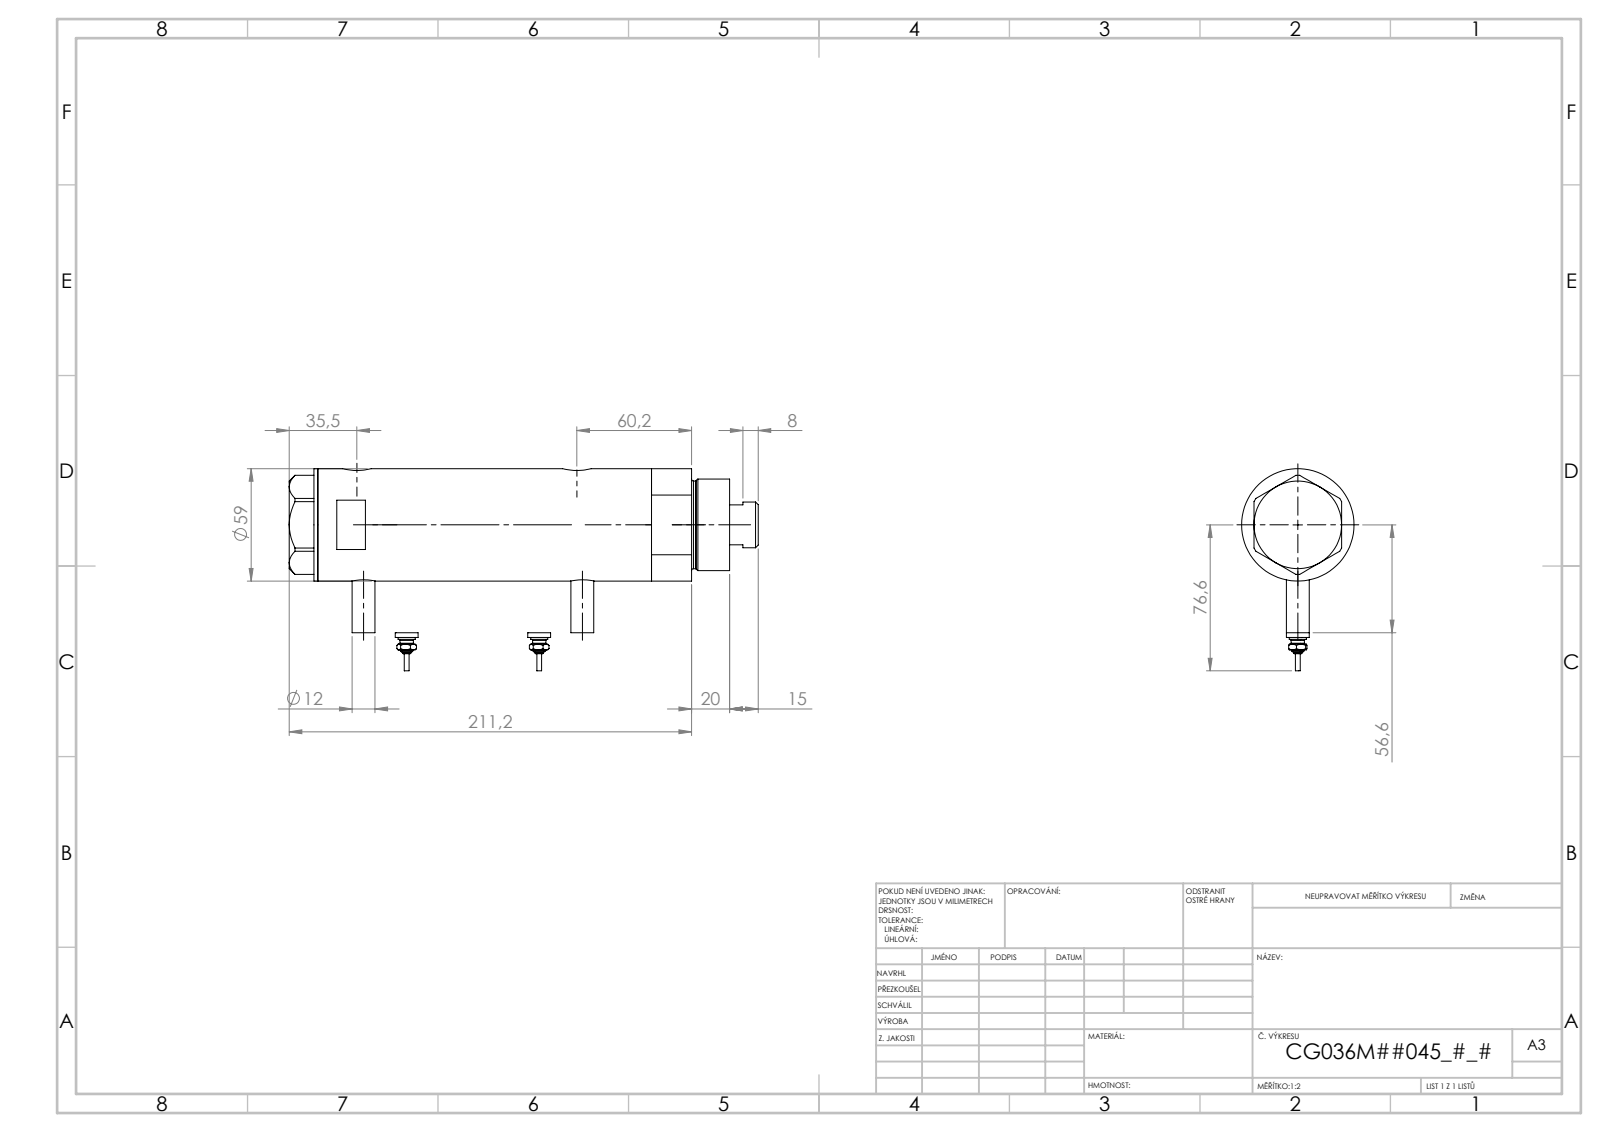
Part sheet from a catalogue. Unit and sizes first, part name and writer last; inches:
Units: inches
Overall size (bounding box): 8.206 × 3.594 × 2.323
Round holes (diameter × count): ⌀0.197 ×2, ⌀0.383 ×2, ⌀0.492 ×2, ⌀0.591 ×2, ⌀0.335 ×1, ⌀0.984 ×1, ⌀1.043 ×1, ⌀1.417 ×1, ⌀1.575 ×1, ⌀2.047 ×1
Round bosses / shafts (diameter × count): ⌀0.472 ×3, ⌀0.354 ×2, ⌀0.276 ×2, ⌀0.171 ×2, ⌀0.094 ×2, ⌀2.323 ×1, ⌀1.89 ×1, ⌀1.811 ×1
Main face-to-face distances: 3.104, 0.591, 4.62, 4.029, 7.615, 1.516, 0.925, 3.104, 1.515, 0.925
Hole centre spacings: 0.114, 0.138, 3.037, 3.152, 3.175, 3.289, 0.114, 0.115
Volume: 28.88 in³ · Surface area: 156.2 in²
Bodies: 6 solids, 232 faces (81 planar, 77 cylindrical, 74 other)
Part name (STEP PRODUCT): V270CG_FRONT; V270CG_MIDDLE; V270CG_SWITCH; V270CG_VC (+1 more)
STEP written by: SolidWorks 2019 (CONFIG_CONTROL_DESIGN)
